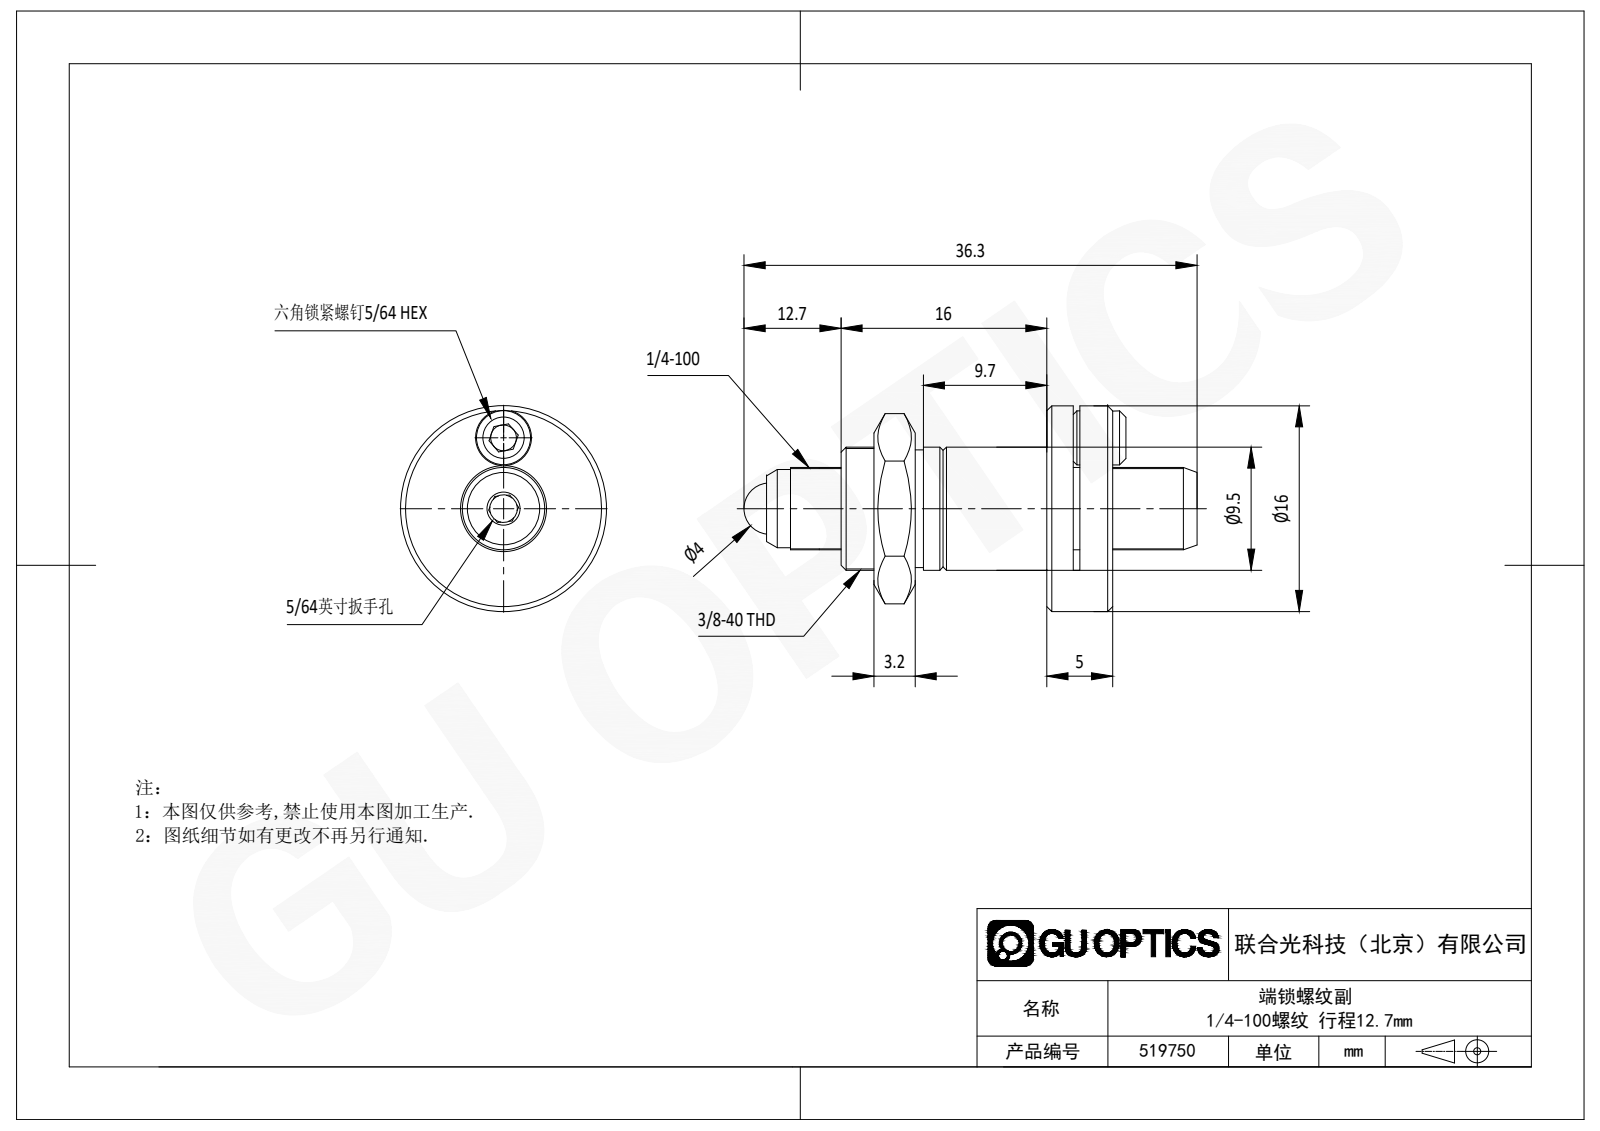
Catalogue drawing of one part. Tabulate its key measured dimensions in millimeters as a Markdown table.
| quantity | value |
| --- | --- |
| part name | AJS100-0.5H |
| STEP written by | SolidWorks 2020 (CONFIG_CONTROL_DESIGN) |
| units | millimeters |
| bodies | 1 solid, 89 faces (48 planar, 17 cylindrical, 24 other) |
| overall size | 36.33 × 16 × 16 |
| volume | 2 639 mm³ |
| surface area | 2 201 mm² |
| round holes (diameter × count) | 1.5 × 1, 2.12 × 1, 6.6 × 1 |
| round bosses / shafts (diameter × count) | 16 × 1, 9.53 × 1, 9.5 × 1, 8.74 × 1, 6.35 × 1, 4.17 × 1 |
| partial cylindrical surfaces (radius × count) | 7.56 × 1, 25.4 × 1 |
| main face-to-face distances | 0.51, 3.05, 2.54, 5, 2.46, 1.95, 12.7, 15.36, 18.41, 15.87 |
